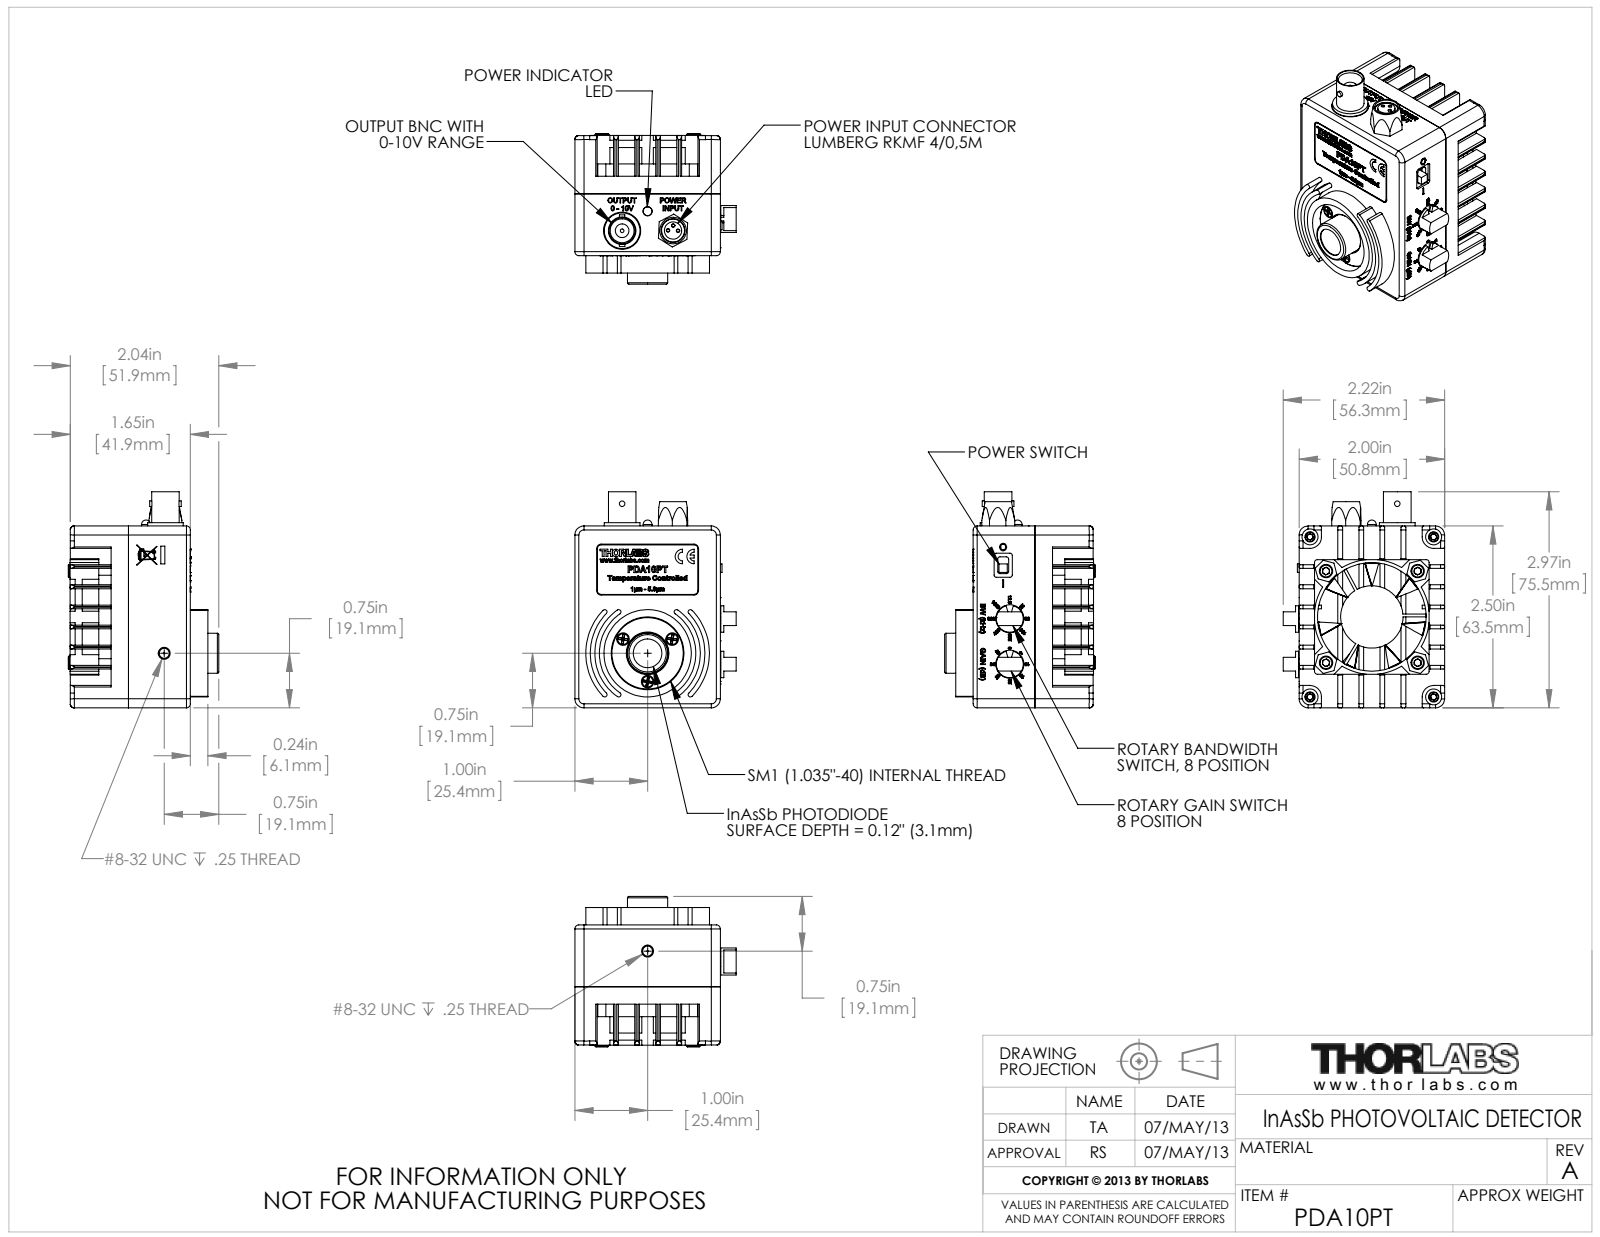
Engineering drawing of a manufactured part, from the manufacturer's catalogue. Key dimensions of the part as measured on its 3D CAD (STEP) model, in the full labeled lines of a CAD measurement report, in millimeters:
Part name (STEP PRODUCT): TTN010624-E0W
STEP written by: SolidWorks 2012 (AUTOMOTIVE_DESIGN)
Units: millimetres
Bodies: 44 solids, 4263 faces (2335 planar, 758 cylindrical, 1170 other)
Overall size (bounding box): 75.5 × 56.3 × 52.6
Volume: 66 070 mm³ · Surface area: 62 280 mm²
Round holes (diameter × count): ⌀0.9 ×20, ⌀2.2 ×11, ⌀0.8 ×10, ⌀2.4 ×9, ⌀1.8 ×8, ⌀1.3 ×7, ⌀1.5 ×6, ⌀1.6 ×6, ⌀0.4 ×4, ⌀2.3 ×4, ⌀2.5 ×4, ⌀2.8 ×4
Round bosses / shafts (diameter × count): ⌀0.5 ×6, ⌀4.6 ×4, ⌀3.6 ×4, ⌀2.8 ×4, ⌀2.2 ×4, ⌀9.4 ×3, ⌀3.7 ×3, ⌀3.5 ×2
Partial cylindrical surfaces — rounded edges, fillets, slot ends (radius × count): R0.5 ×48, R0.2 ×33, R2.5 ×22, R0.1 ×20, R0.8 ×16, R1.4 ×8, R0.4 ×4, R1 ×4
Main face-to-face distances: 1.6, 7.6, 1.3, 6.1, 20.3, 7.4, 8.1, 21.6, 27.7, 14.2
Hole centre spacings: 2.5, 5.7, 3.6, 8.1, 11.4, 1.8, 5.1, 8.9
